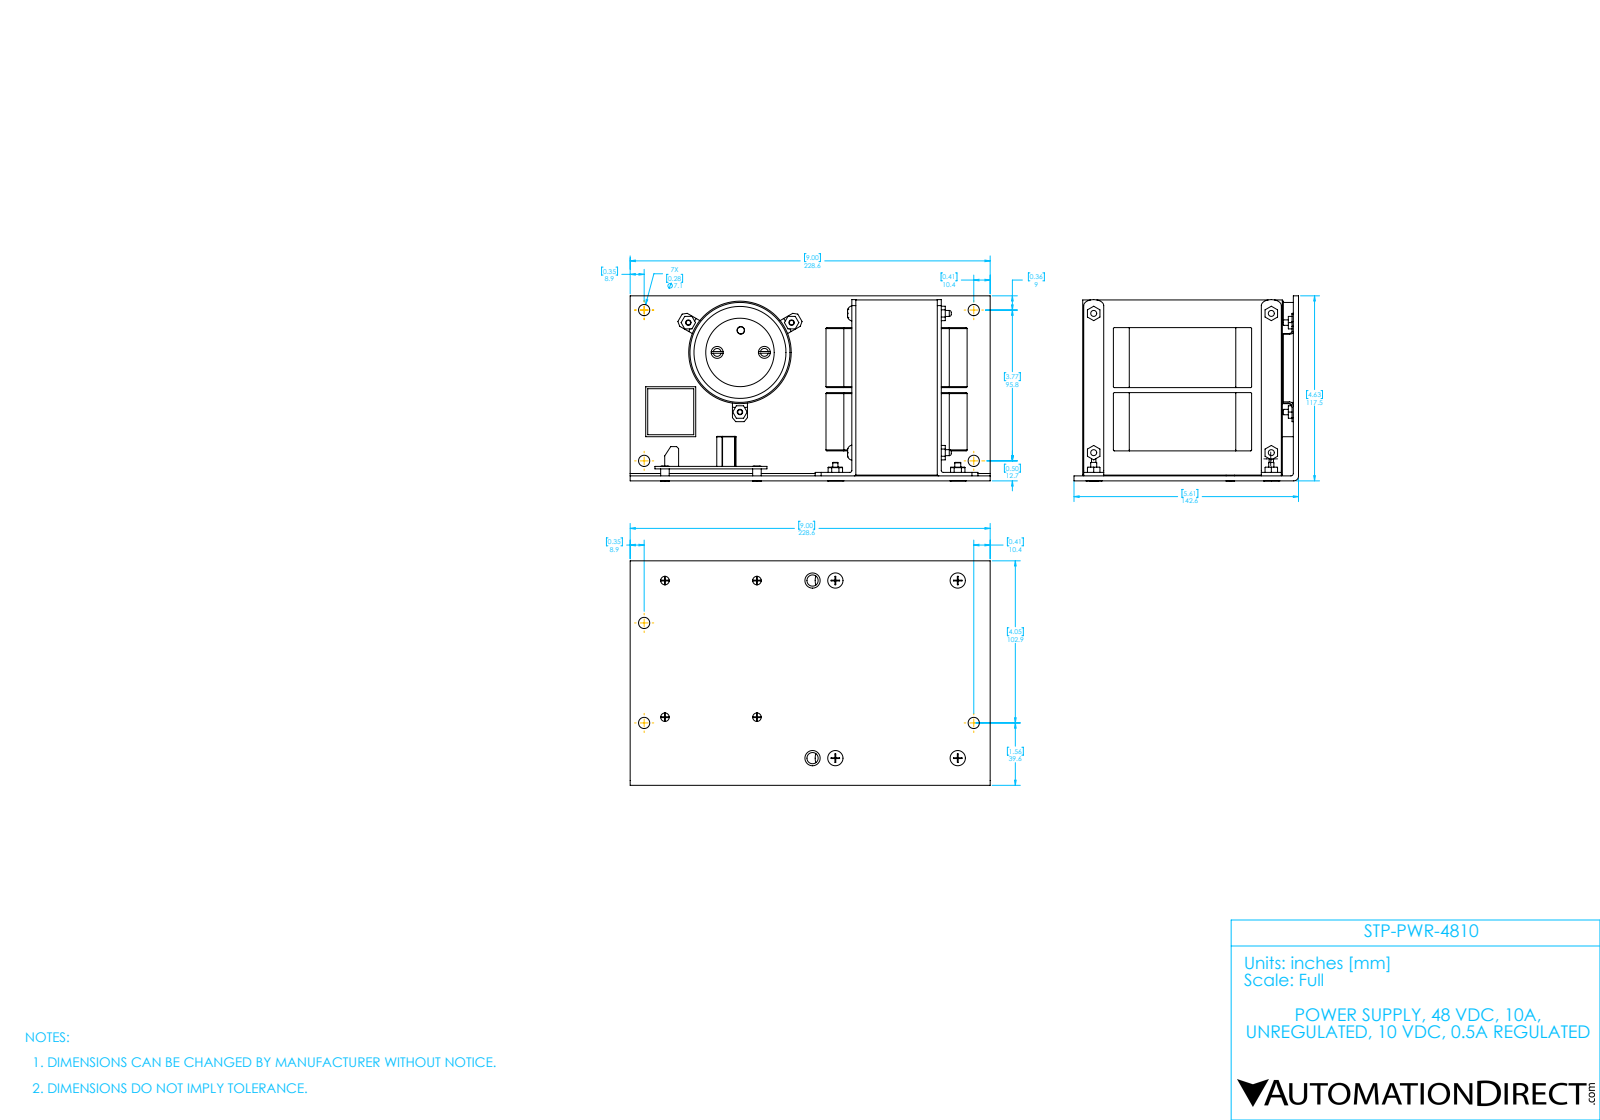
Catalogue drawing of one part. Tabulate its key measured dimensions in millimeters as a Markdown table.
| quantity | value |
| --- | --- |
| part name | STP-PWR-4810 |
| STEP written by | SolidWorks 2017 (AUTOMOTIVE_DESIGN) |
| units | millimeters |
| bodies | 2 solids, 825 faces (472 planar, 251 cylindrical, 102 other) |
| overall size | 228.6 × 142.6 × 117.6 |
| volume | 1 562 000 mm³ |
| surface area | 236 700 mm² |
| round holes (diameter × count) | 7.1 × 9, 2.7 × 7 |
| round bosses / shafts (diameter × count) | 3.8 × 5, 9.7 × 4, 5.4 × 4, 3.5 × 3, 3.3 × 3, 7.6 × 2, 3.1 × 2, 2.7 × 2 |
| partial cylindrical surfaces (radius × count) | 0.3 × 22, 0.6 × 16, 0.3 × 5, 1.3 × 4, 1.4 × 4, 2.7 × 4, 2.7 × 4, 10.9 × 4 |
| main face-to-face distances | 3.2, 3.3, 19, 70.7, 7.6, 4.4, 3.7, 0.5, 4, 114.9 |
| hole center spacings | 6.1, 209.3, 27.9, 29.1, 57.1, 95.8, 230.2, 6.1 |
